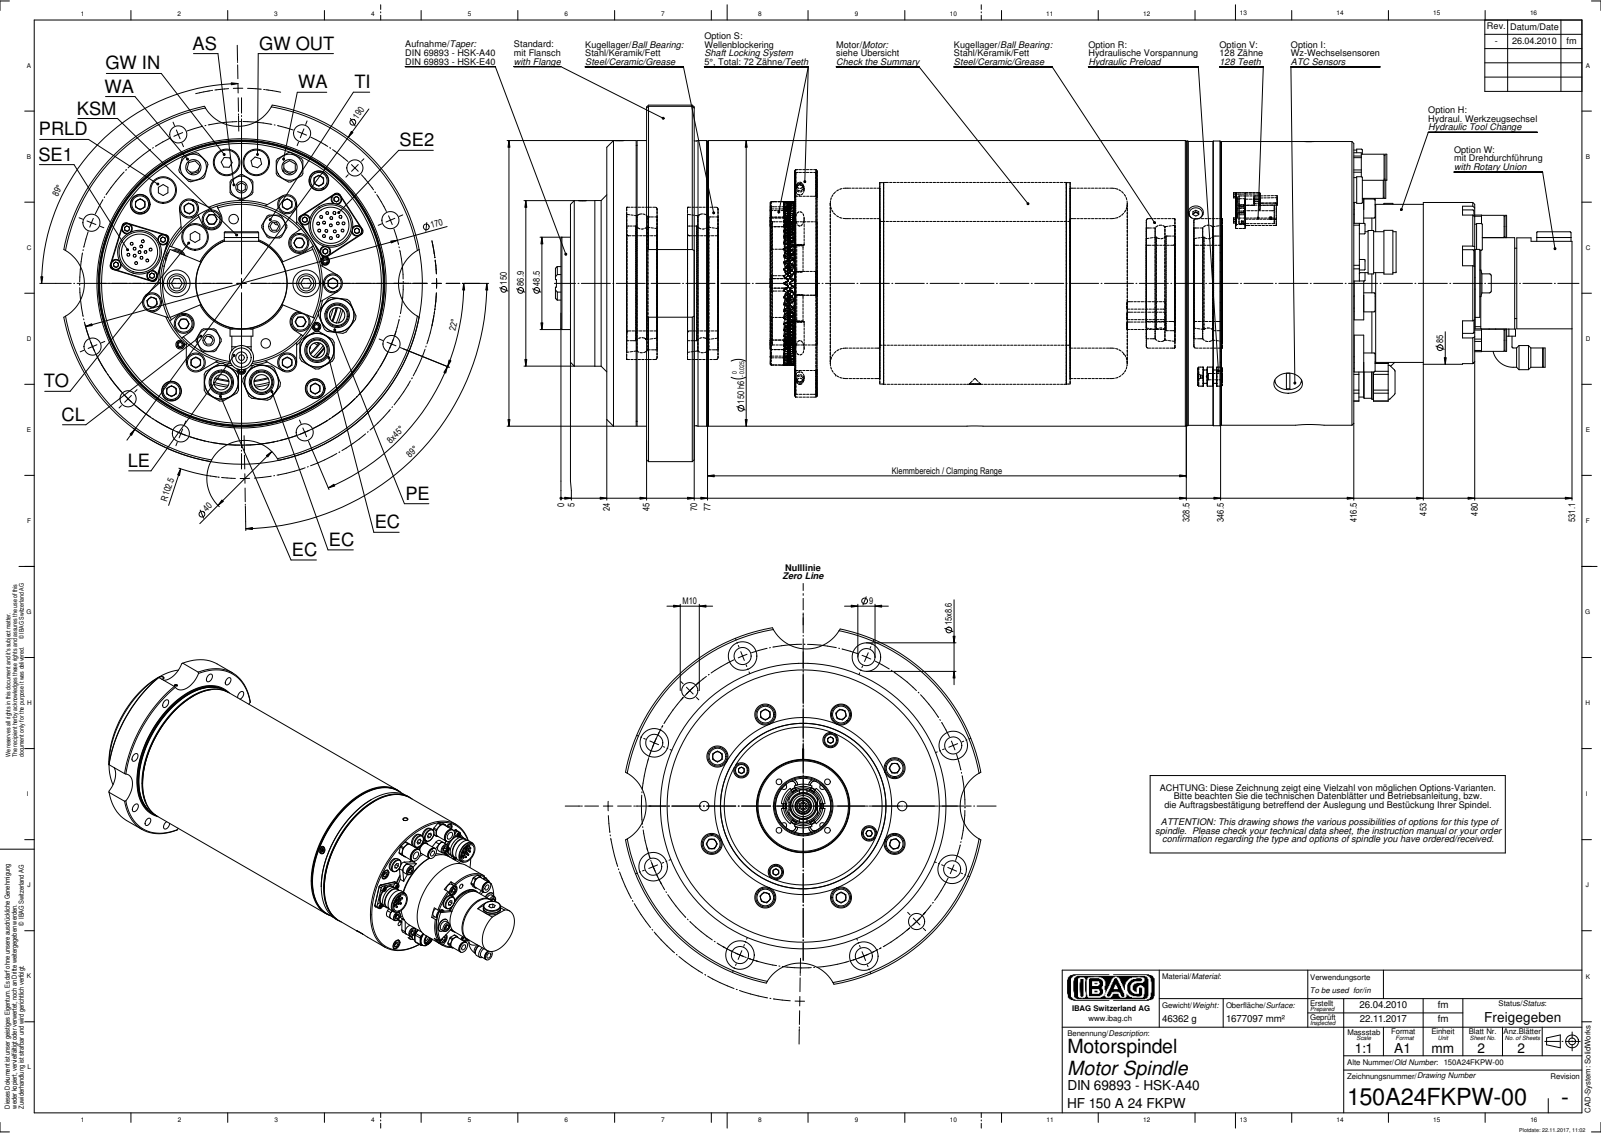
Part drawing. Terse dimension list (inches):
name: 150A24FKPW-00
written by: SolidWorks 2010 (CONFIG_CONTROL_DESIGN)
unit: in
bodies: 0 solids, 1354 faces (569 planar, 511 cylindrical, 274 other)
size: 23.317 × 7.426 × 7.414
holes: 12× ⌀0.315, 12× ⌀0.591, 8× ⌀0.354, 8× ⌀0.433, 4× ⌀0.236, 4× ⌀0.409, 4× ⌀0.421, 4× ⌀0.638, 3× ⌀0.197, 2× ⌀0.177, 2× ⌀0.335, 2× ⌀0.748
bosses: 29× ⌀0.059, 14× ⌀0.394, 8× ⌀0.217, 6× ⌀0.551, 4× ⌀0.701, 4× ⌀0.661, 4× ⌀0.614, 3× ⌀0.512
rounds: 12× R0.039, 6× R0.217, 4× R0.177, 4× R0.39, 3× R0.26, 2× R0.305, 2× R0.787, 1× R0.571
face distances: 13.642, 0.984, 0.831, 1.815, 15.457, 14.626, 11.992, 11.161, 10.177, 3.465
hole spacings: 3.346, 2.047, 2.37, 2.406, 3.907, 3.938, 4.999, 5.016
